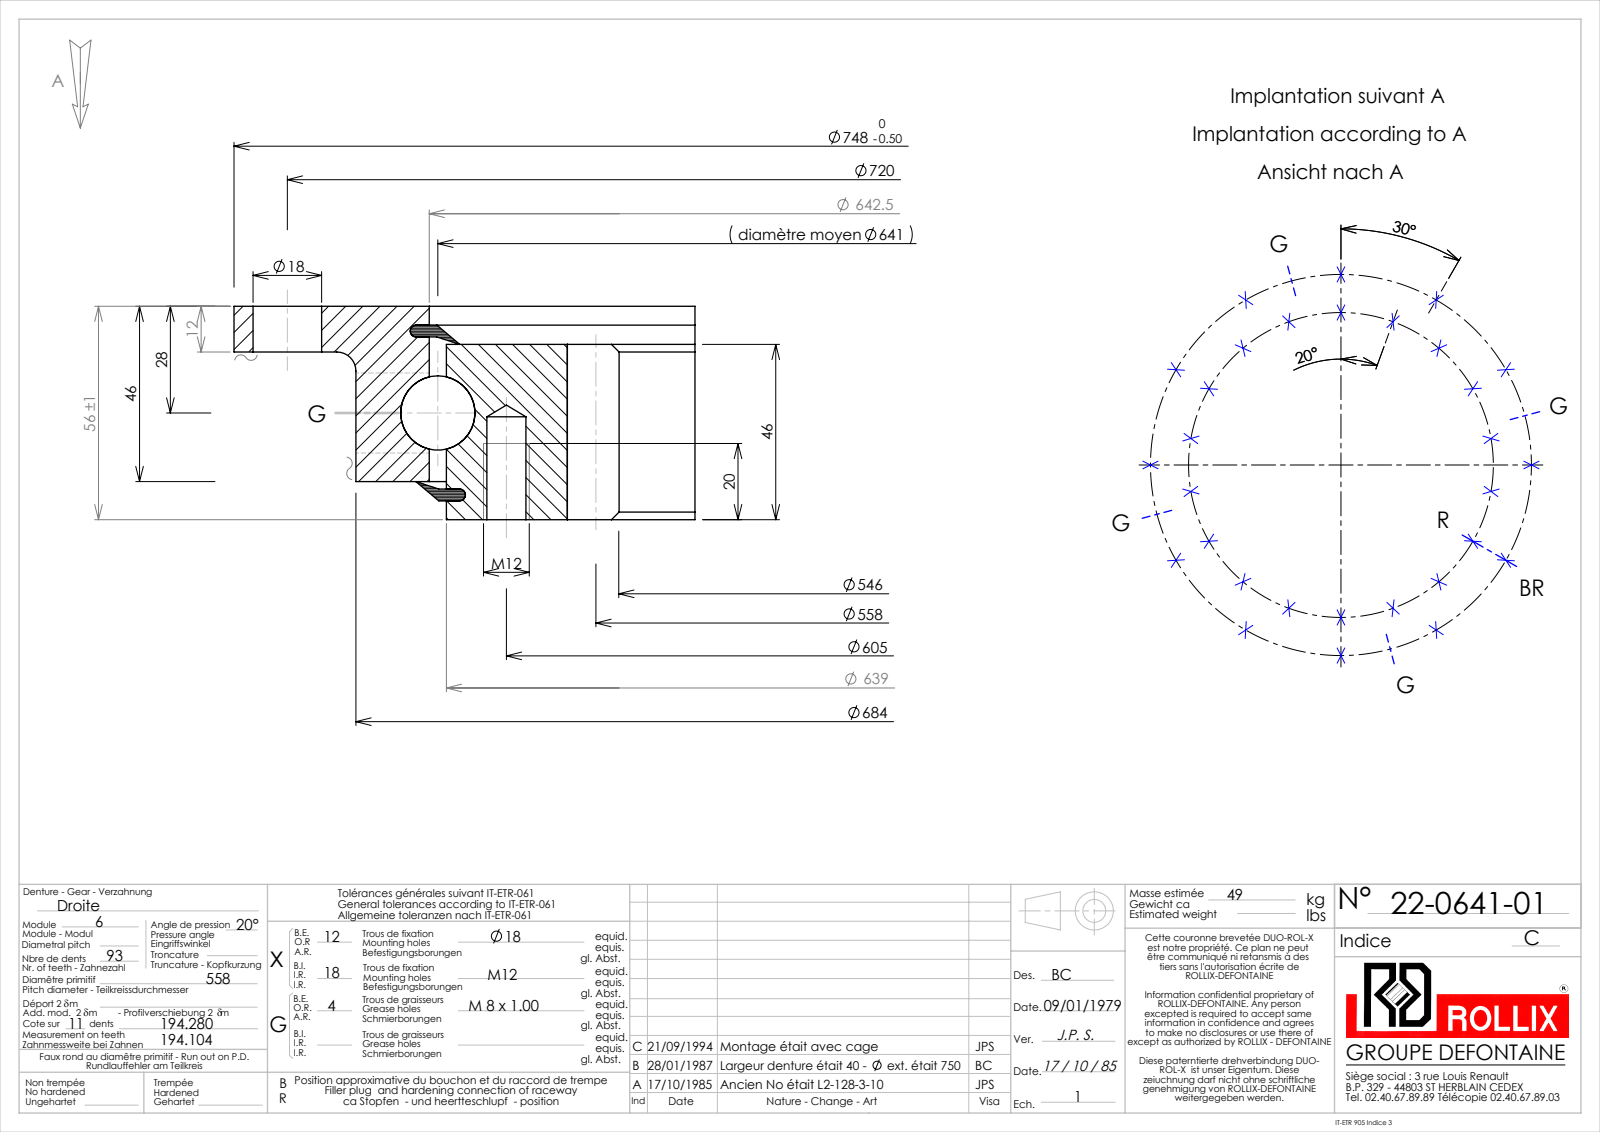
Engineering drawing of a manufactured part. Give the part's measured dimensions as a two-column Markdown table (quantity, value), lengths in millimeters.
| quantity | value |
| --- | --- |
| part name | 22-0641-01 |
| STEP written by | SolidWorks 2016 (CONFIG_CONTROL_DESIGN) |
| units | millimeters |
| bodies | 9 solids, 811 faces (239 planar, 279 cylindrical, 293 other) |
| overall size | 748 × 748 × 56 |
| volume | 5 639 000 mm³ |
| surface area | 1 016 000 mm² |
| round holes (diameter × count) | 10.25 × 18, 18 × 12, 7 × 4, 645.5 × 1 |
| round bosses / shafts (diameter × count) | 8 × 4, 748 × 1, 684 × 1, 636.5 × 1 |
| partial cylindrical surfaces (radius × count) | 273 × 1, 286.5 × 1 |
| main face-to-face distances | 10, 46, 56, 44, 2, 12, 34, 36, 8.05, 47.95 |
| hole center spacings | 105.06, 206.92, 302.5, 568.51, 523.94, 180.24, 186.35, 232.94 |
